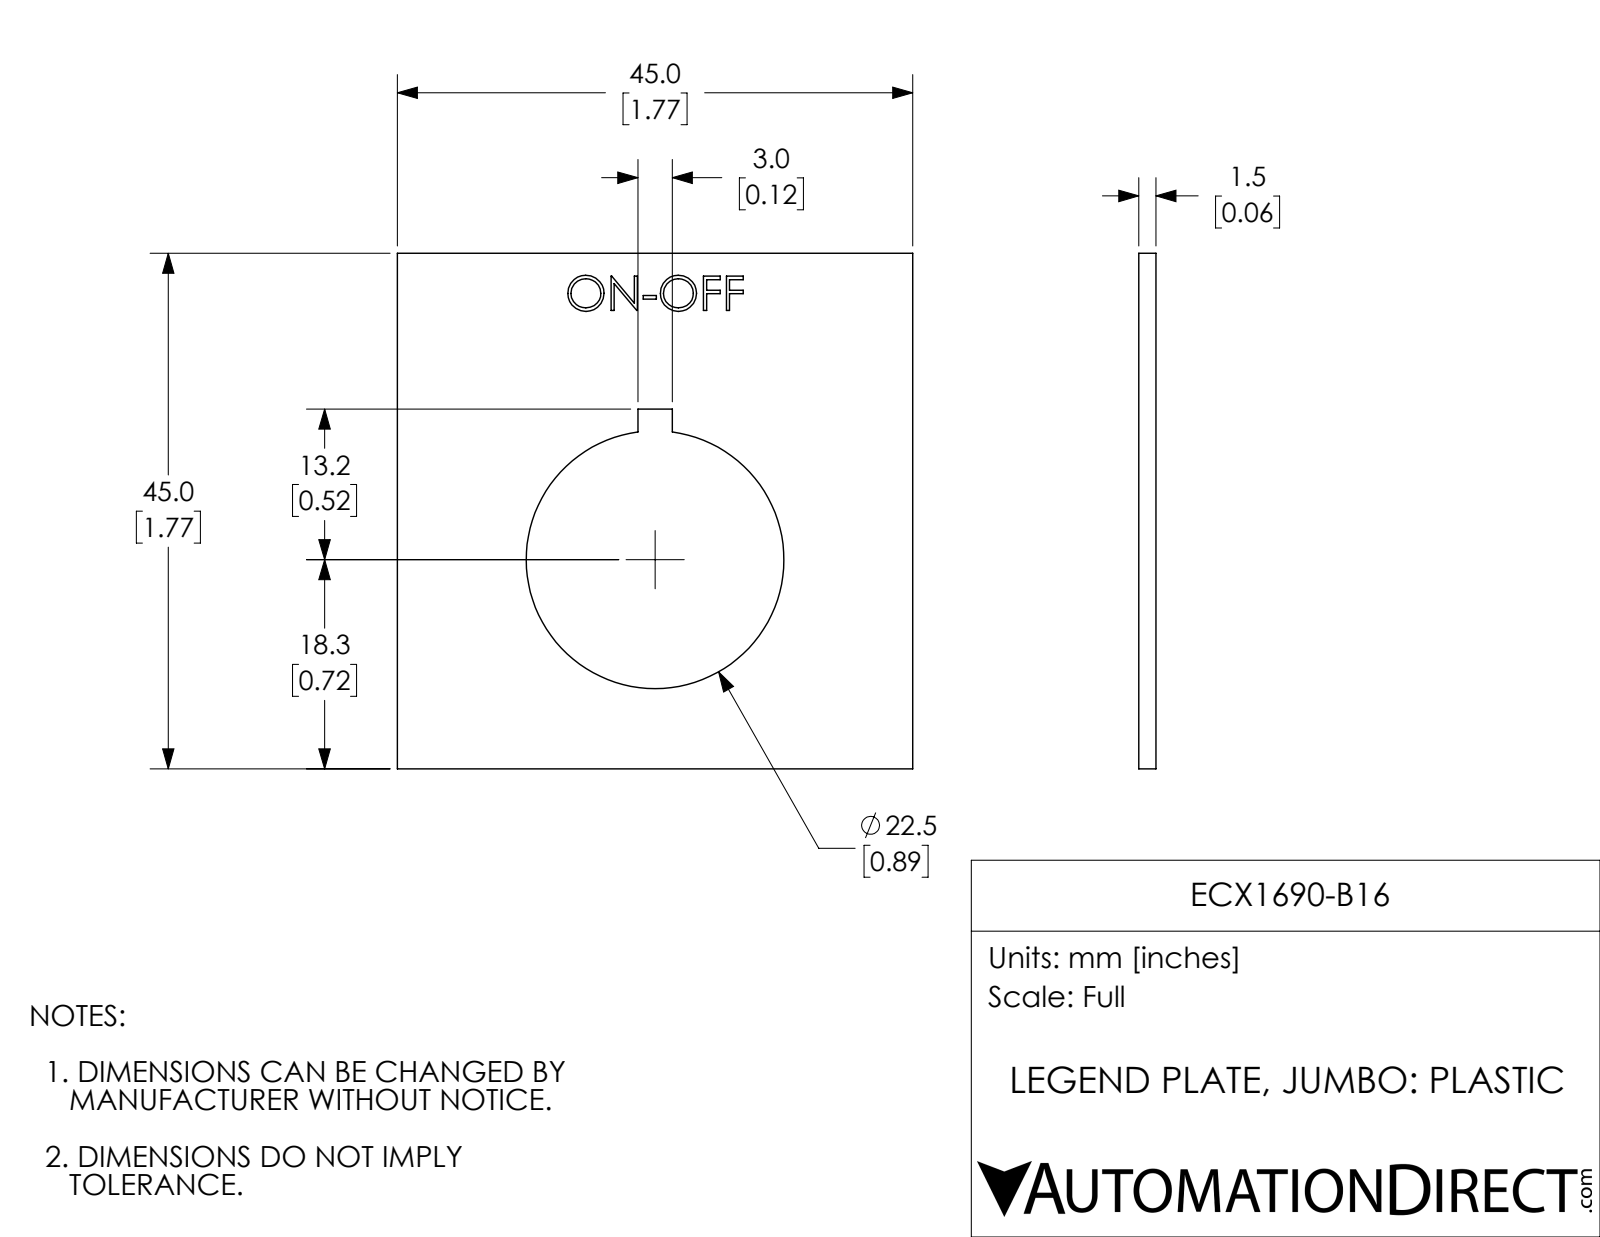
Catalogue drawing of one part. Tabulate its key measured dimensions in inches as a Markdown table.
| quantity | value |
| --- | --- |
| part name | ECX1690-B16 |
| STEP written by | SolidWorks 2018 (AUTOMOTIVE_DESIGN) |
| units | inches |
| bodies | 1 solid, 70 faces (51 planar, 3 cylindrical, 16 other) |
| overall size | 1.772 × 1.772 × 0.059 |
| volume | 0.148 in³ |
| surface area | 5.622 in² |
| round holes (diameter × count) | 0.886 × 1 |
| main face-to-face distances | 0.059, 1.772, 0.058, 0.827, 0.945, 1.236, 0.535, 0.118, 0.079, 0.091 |
